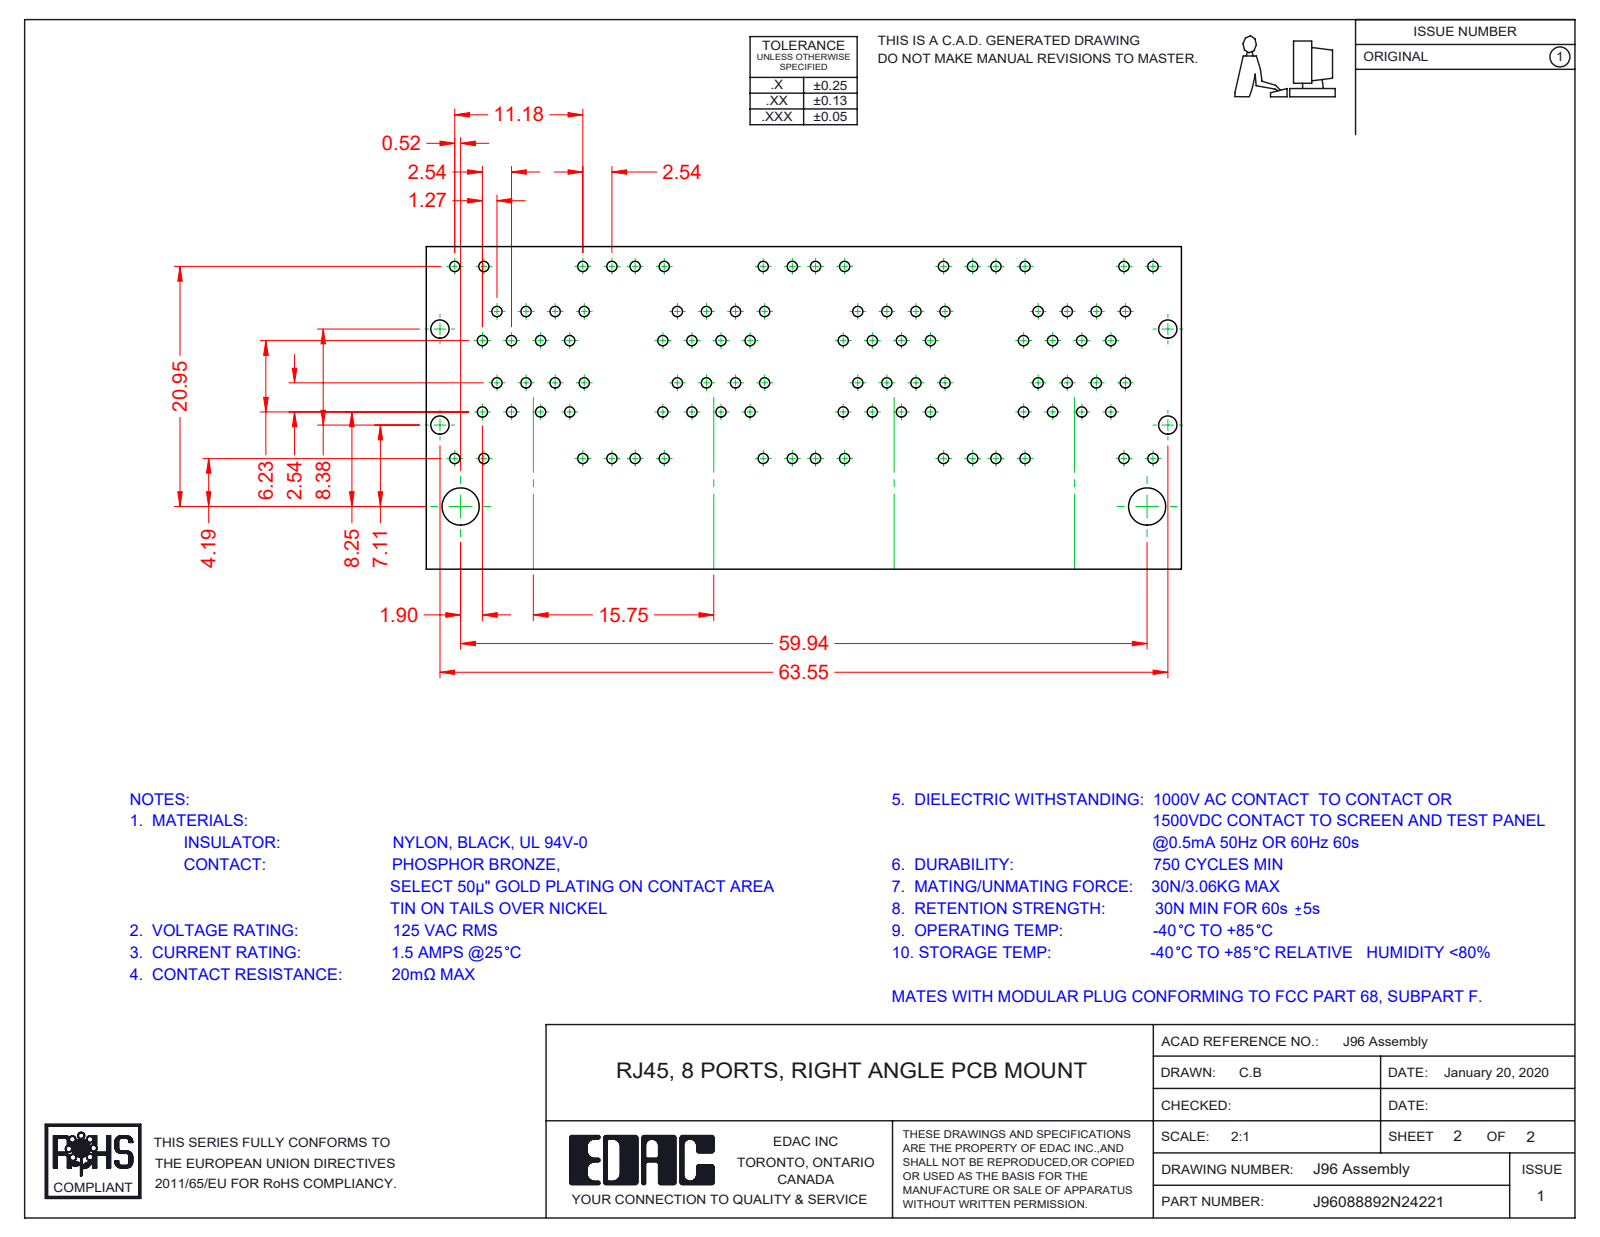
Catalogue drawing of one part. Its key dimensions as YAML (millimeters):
part_name: "96 LED LH Lower_2-Red; 96 Insulator Insert; J96088892N24221; 96 Contact Lock Upper (+8 more)"
step_written_by: "SolidWorks 2016 (CONFIG_CONTROL_DESIGN)"
units: millimeters
bodies: {solids: 96, faces: 7804, planar: 6105, cylindrical: 1388, other: 311}
overall_size: [67.35, 31.38, 28.68]
volume: 24149
surface_area: 63596
round_holes:
  - {diameter: 1.7, count: 3}
round_bosses_or_shafts:
  - {diameter: 1.68, count: 3}
partial_cylinders:
  - {radius: 0.25, count: 124}
  - {radius: 0.35, count: 73}
  - {radius: 1, count: 72}
  - {radius: 0.5, count: 49}
  - {radius: 0.91, count: 32}
  - {radius: 0.2, count: 27}
  - {radius: 0.27, count: 14}
  - {radius: 0.7, count: 11}
face_to_face_distances: [15.75, 0.35, 9.95, 1.17, 1.6, 0.54, 9.98, 10.18, 12.67, 3.37]
hole_center_spacings: [15.75, 31.5]
